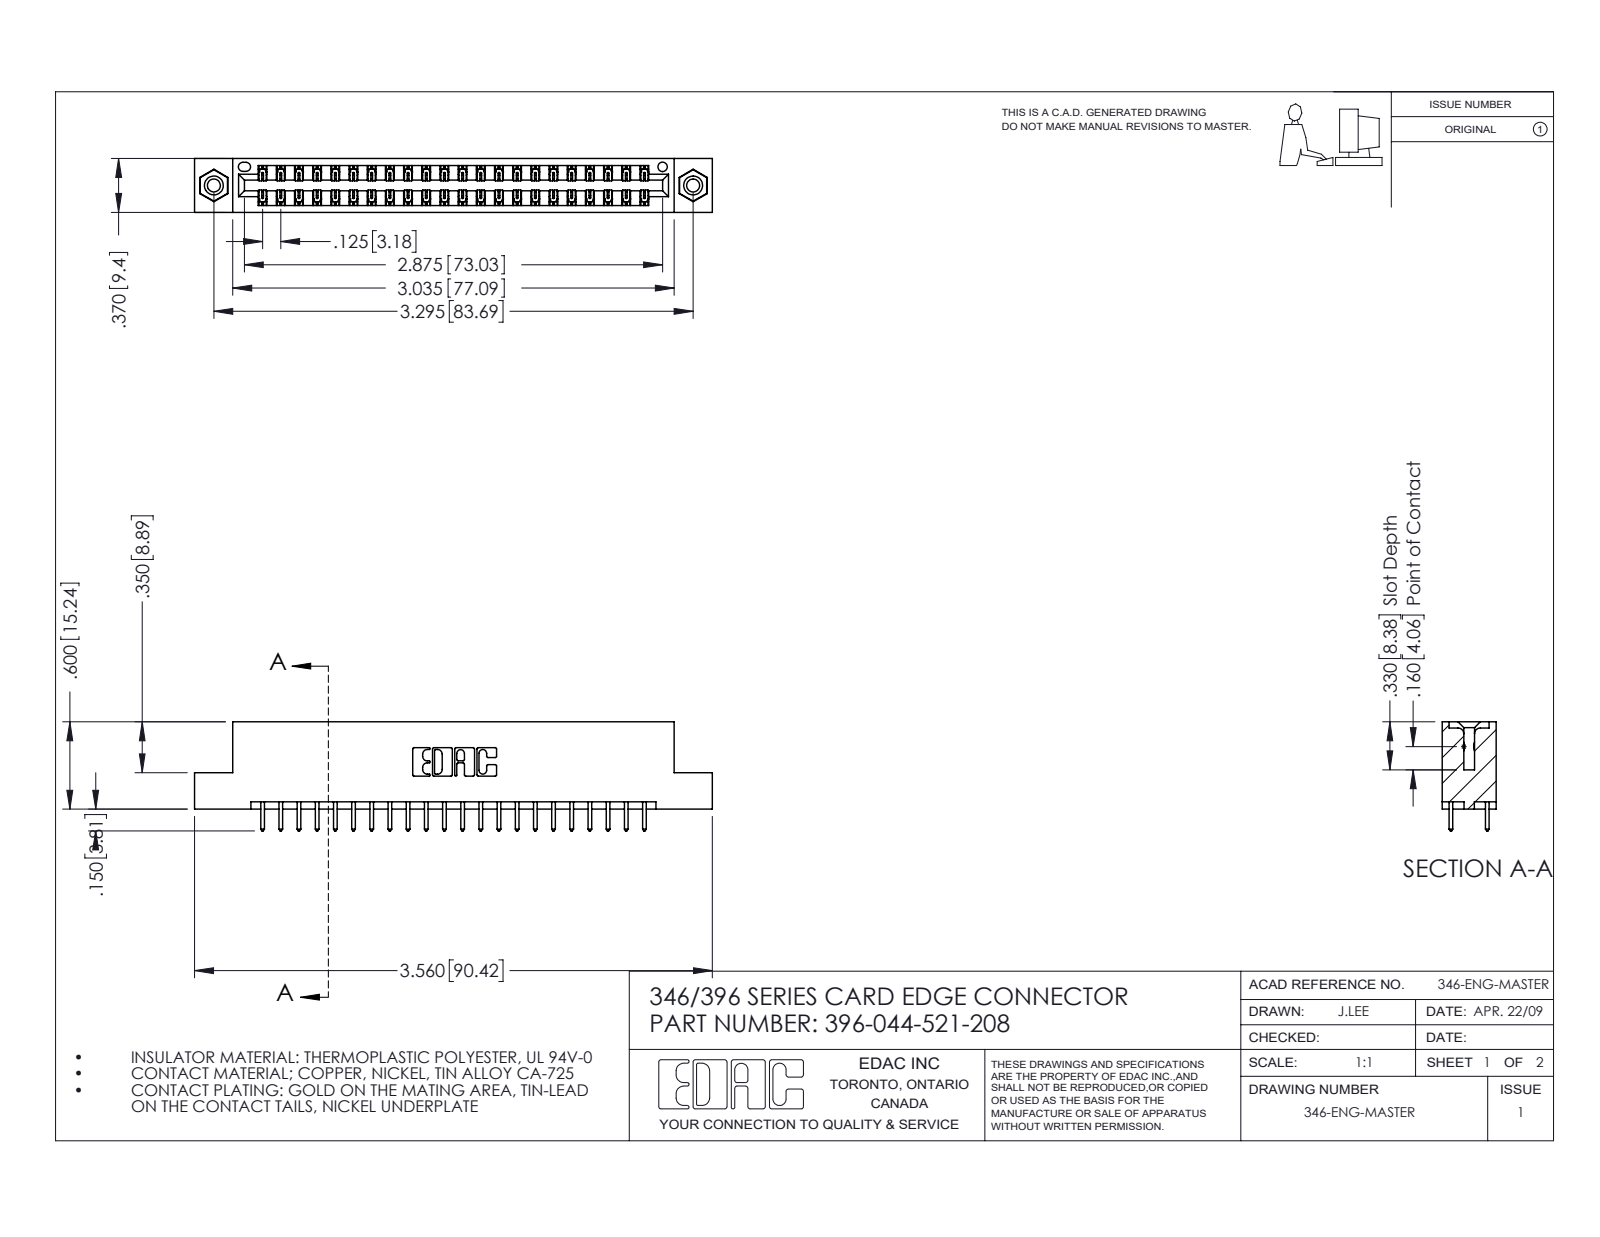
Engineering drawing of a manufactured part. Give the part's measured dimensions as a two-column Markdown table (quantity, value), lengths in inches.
| quantity | value |
| --- | --- |
| part name | 345-292-001_345-293-121; 346 Part_Flush Mounting Lugs - 0.156 Dia-TI; 345-250-001_345-250-003-102; 396-044-521-208 |
| STEP written by | SolidWorks 2016 (CONFIG_CONTROL_DESIGN) |
| units | inches |
| bodies | 47 solids, 2470 faces (1648 planar, 806 cylindrical, 16 other) |
| overall size | 3.56 × 0.75 × 0.37 |
| volume | 0.527 in³ |
| surface area | 17.76 in² |
| round holes (diameter × count) | 0.089 × 2, 0.125 × 2, 0.156 × 2, 0.064 × 1 |
| round bosses / shafts (diameter × count) | 0.155 × 2 |
| partial cylindrical surfaces (radius × count) | 0.006 × 66, 0.01 × 44, 0.01 × 22, 0.007 × 6, 0.031 × 6, 0.026 × 3, 0.014 × 2, 0.022 × 2 |
| main face-to-face distances | 0.048, 0.322, 0.25, 0.37, 0.072, 0.298, 0.025, 0.275, 0.148, 0.222 |
| hole center spacings | 0.246, 3.087, 3.295 |
